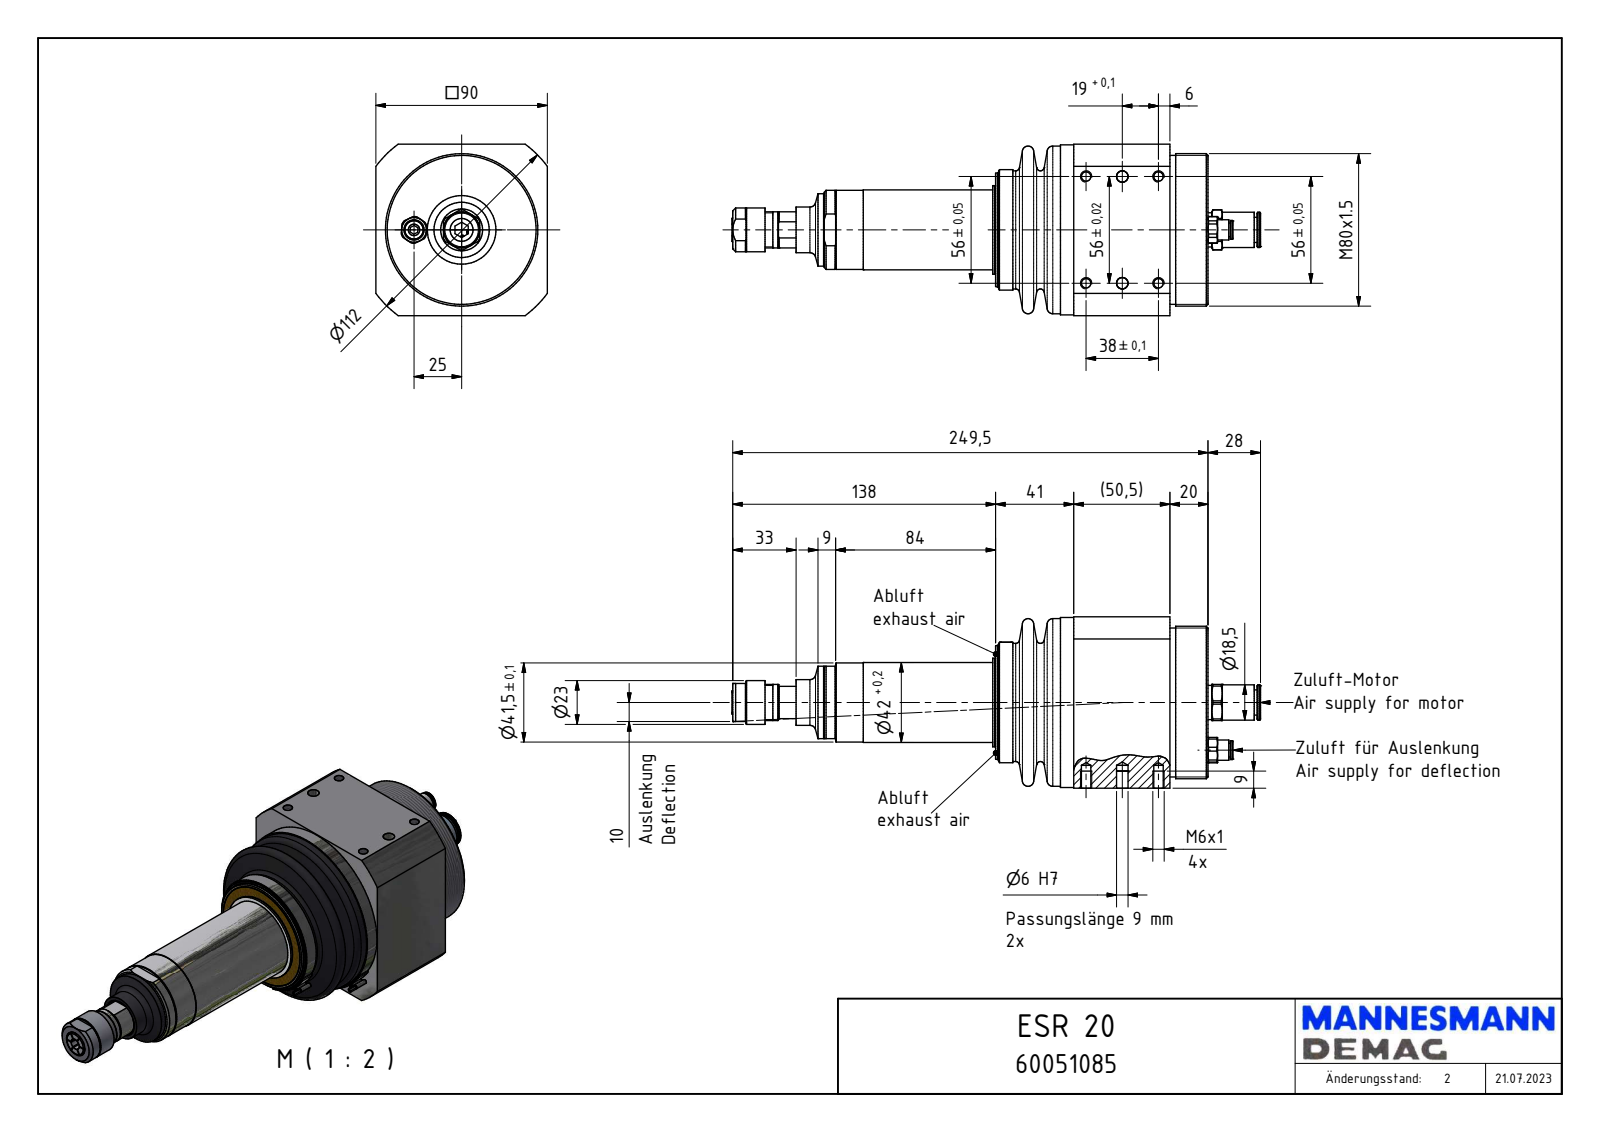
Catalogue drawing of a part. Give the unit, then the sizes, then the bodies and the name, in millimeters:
Units: millimetres
Overall size (bounding box): 277.47 × 90 × 90
Round holes (diameter × count): ⌀6 ×16, ⌀4.92 ×4, ⌀4 ×2, ⌀6 ×2, ⌀1.6 ×1, ⌀2.5 ×1, ⌀6.1 ×1, ⌀8.38 ×1, ⌀8.5 ×1, ⌀8.57 ×1, ⌀9.1 ×1, ⌀10.5 ×1
Round bosses / shafts (diameter × count): ⌀89.2 ×1, ⌀86.4 ×1, ⌀78.18 ×1, ⌀73.28 ×1, ⌀63.2 ×1, ⌀60 ×1, ⌀59.5 ×1, ⌀58.1 ×1
Partial cylindrical surfaces — rounded edges, fillets, slot ends (radius × count): R4.65 ×98, R0.5 ×8, R1 ×8, R1.1 ×8, R7 ×7, R10 ×6, R18.09 ×6, R33.72 ×6
Main face-to-face distances: 90, 54, 20, 12.99, 10, 57.51, 70.5, 48.5, 22, 35.51
Hole centre spacings: 15, 7.76, 21.21, 25.98, 28.98, 30, 8.69, 13.04
Volume: 1 046 000 mm³ · Surface area: 256 297 mm²
Bodies: 18 solids, 959 faces (264 planar, 450 cylindrical, 245 other)
Part name (STEP PRODUCT): ESR 20_60051085
STEP written by: Autodesk Inventor 2018 (CONFIG_CONTROL_DESIGN)
